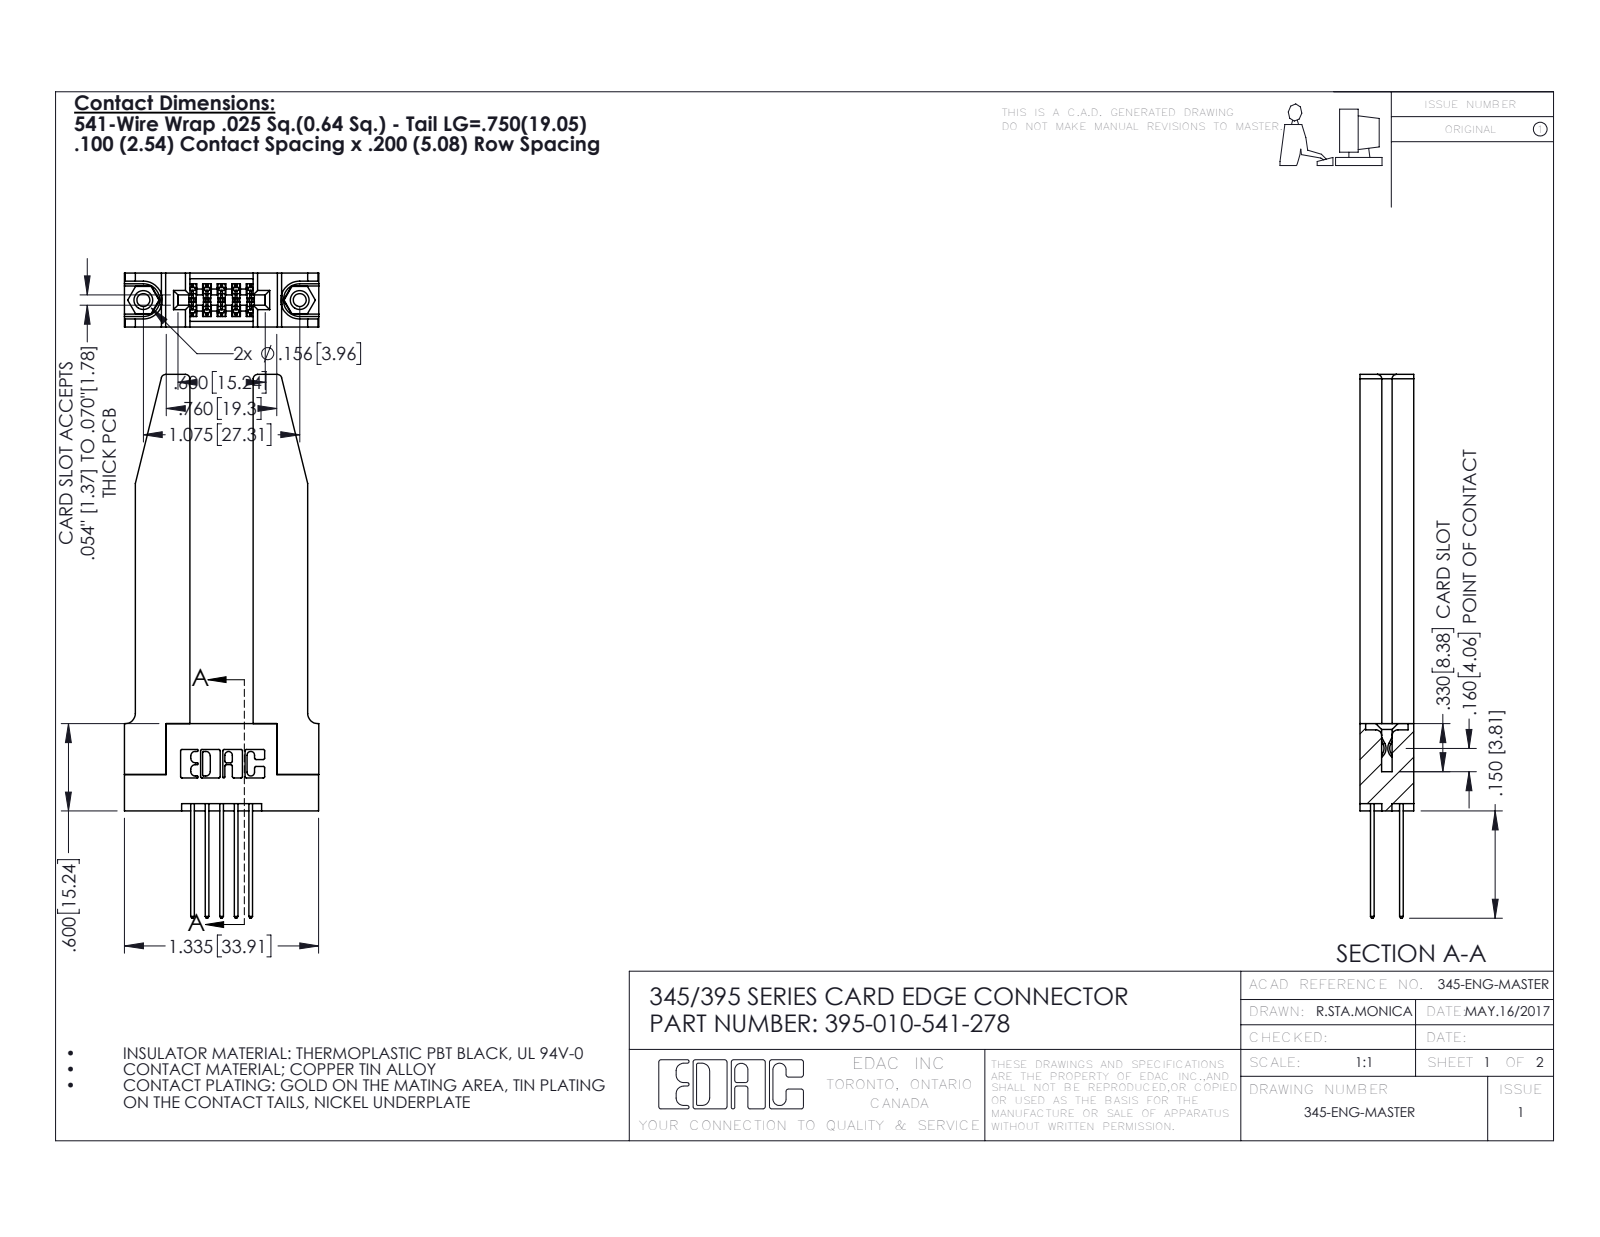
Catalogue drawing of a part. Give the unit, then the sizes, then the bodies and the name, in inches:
Units: inches
Overall size (bounding box): 3.737 × 1.336 × 0.37
Round holes (diameter × count): ⌀0.089 ×2, ⌀0.125 ×2, ⌀0.156 ×2, ⌀0.064 ×1
Round bosses / shafts (diameter × count): ⌀0.155 ×2
Partial cylindrical surfaces — rounded edges, fillets, slot ends (radius × count): R0.01 ×22, R0.006 ×15, R0.01 ×10, R0.03 ×8, R0.007 ×6, R0.031 ×6, R0.026 ×3, R0.014 ×2
Main face-to-face distances: 0.37, 0.15, 0.072, 0.148, 0.22, 0.077, 0.298, 0.2, 0.435, 0.098
Hole centre spacings: 0.27, 0.847, 1.075
Volume: 0.658 in³ · Surface area: 16.8 in²
Bodies: 15 solids, 860 faces (552 planar, 256 cylindrical, 52 other)
Part name (STEP PRODUCT): 345-220-078_345-220-078; 345-250-001_345-250-001-102; 345 Part_Flush Mounting Lugs - 0.156 Dia-TH; 395-010-541-278 (+1 more)
STEP written by: SolidWorks 2016 (CONFIG_CONTROL_DESIGN)
